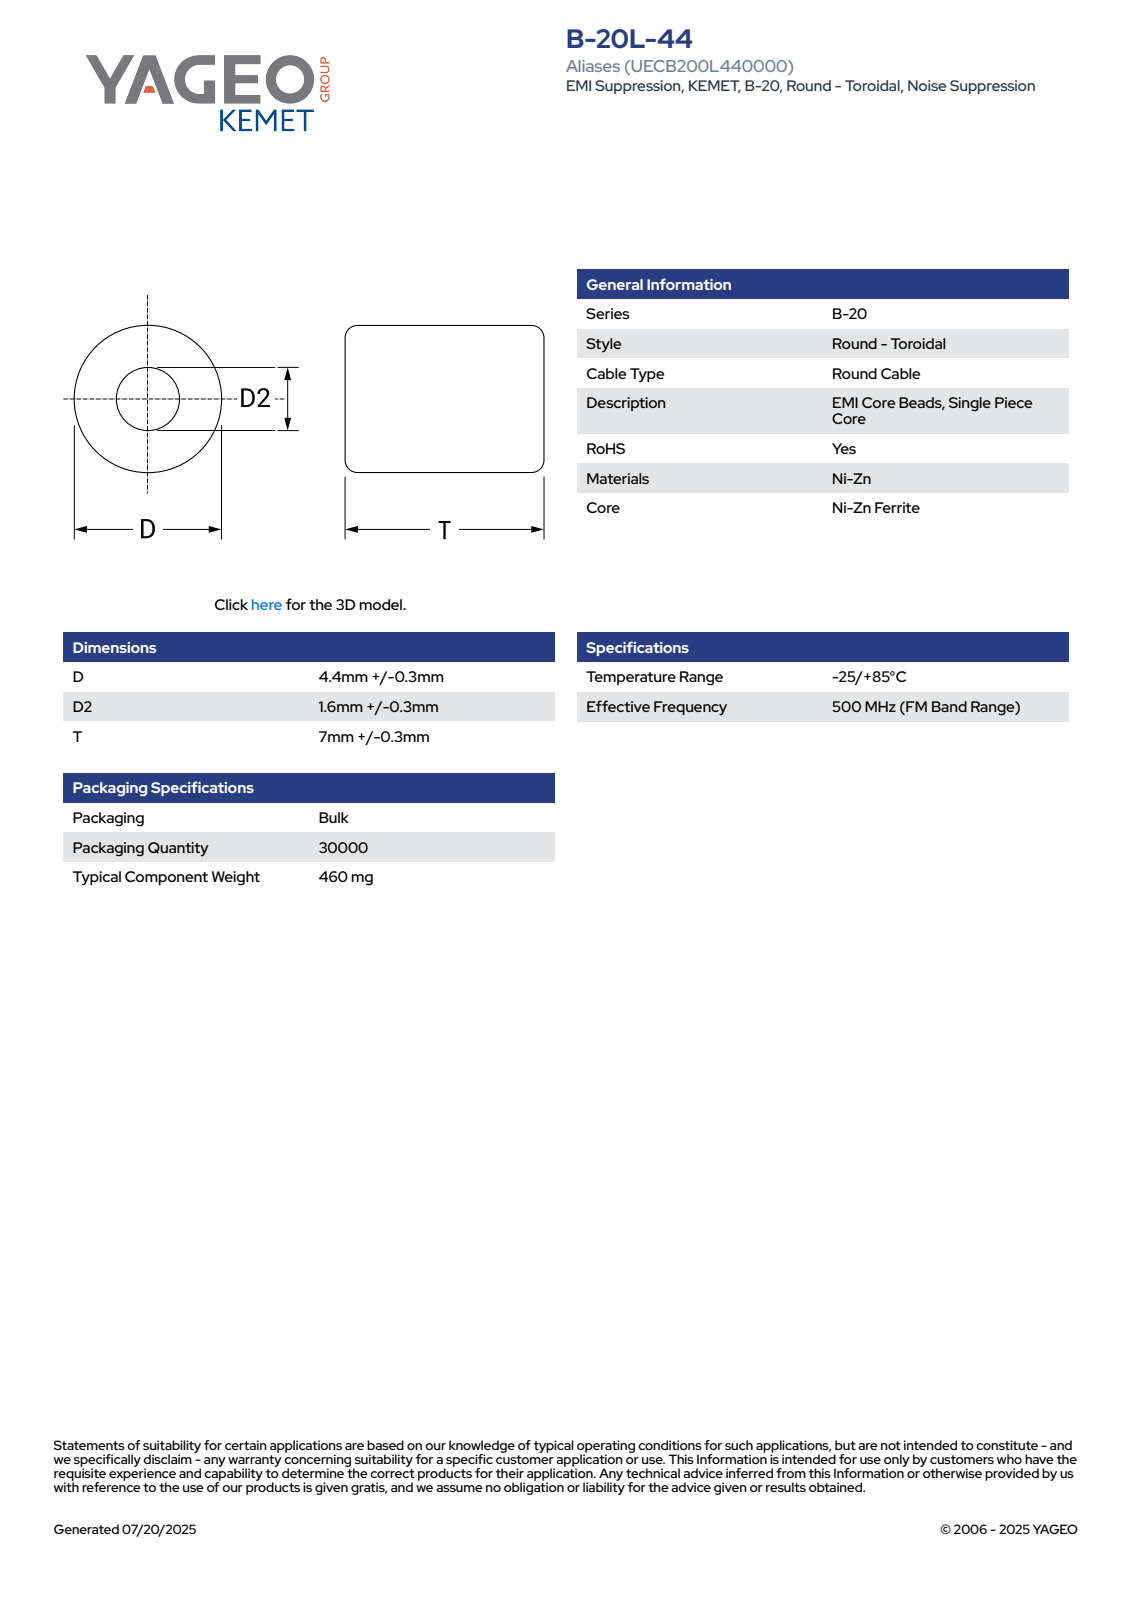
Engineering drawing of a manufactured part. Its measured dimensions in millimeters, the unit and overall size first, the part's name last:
Units: millimetres
Overall size (bounding box): 7.3 × 4.71 × 4.7
Round holes (diameter × count): ⌀1.6 ×1
Round bosses / shafts (diameter × count): ⌀4.7 ×1
Partial cylindrical surfaces — rounded edges, fillets, slot ends (radius × count): R2.36 ×1
Main face-to-face distances: 7.3, 3.46, 3.84, 0.38, 3.53, 3.77, 0.31, 3.7, 3.6, 3.63
Volume: 112 mm³ · Surface area: 174 mm²
Bodies: 1 solid, 66 faces (25 planar, 7 cylindrical, 34 other)
Part name (STEP PRODUCT): EC_KBCH_D4.7D21.6T7.3
STEP written by: SolidWorks 2021 (AUTOMOTIVE_DESIGN)
